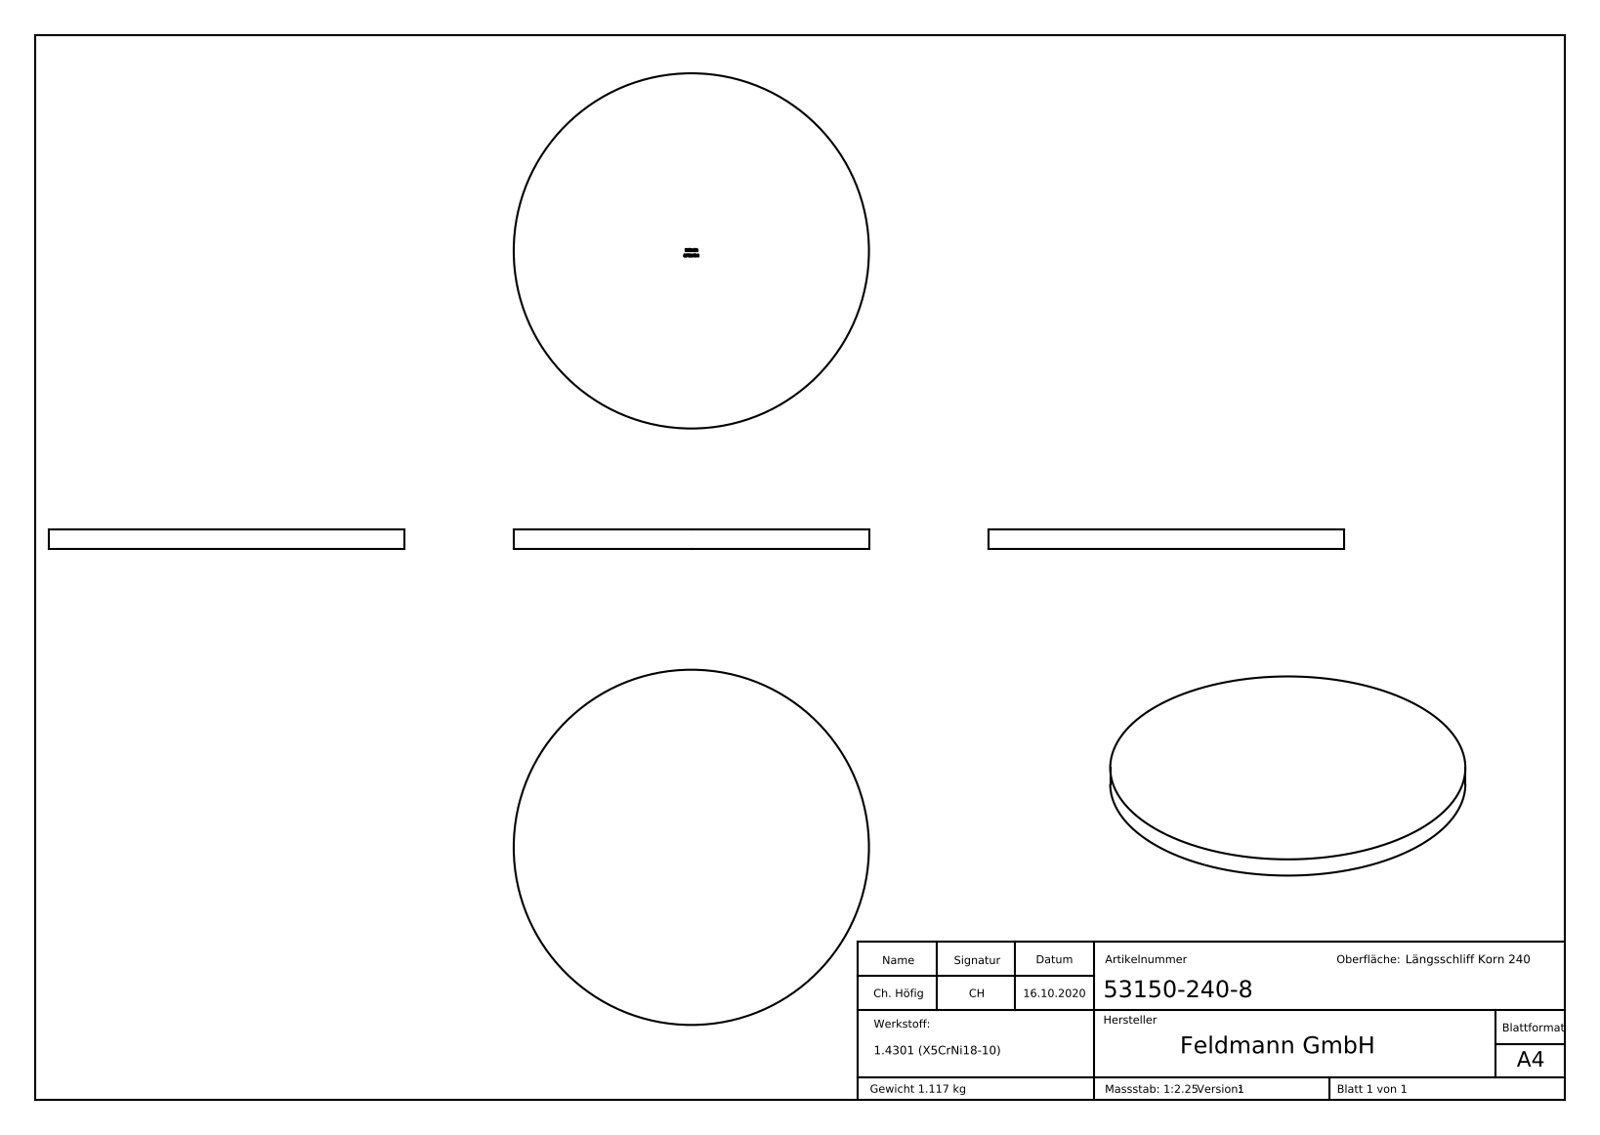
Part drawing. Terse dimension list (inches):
name: 53150-240-8
written by: SolidWorks 2018 (CONFIG_CONTROL_DESIGN)
unit: in
bodies: 1 solid, 252 faces (131 planar, 2 cylindrical, 119 other)
size: 5.906 × 5.906 × 0.315
volume: 8.627 in³; area: 60.63 in²
bosses: 1× ⌀5.906
face distances: 0.315, 0.311, 0.033, 0.07, 0.103, 0.03, 0.04, 0.096, 0.031, 0.037
